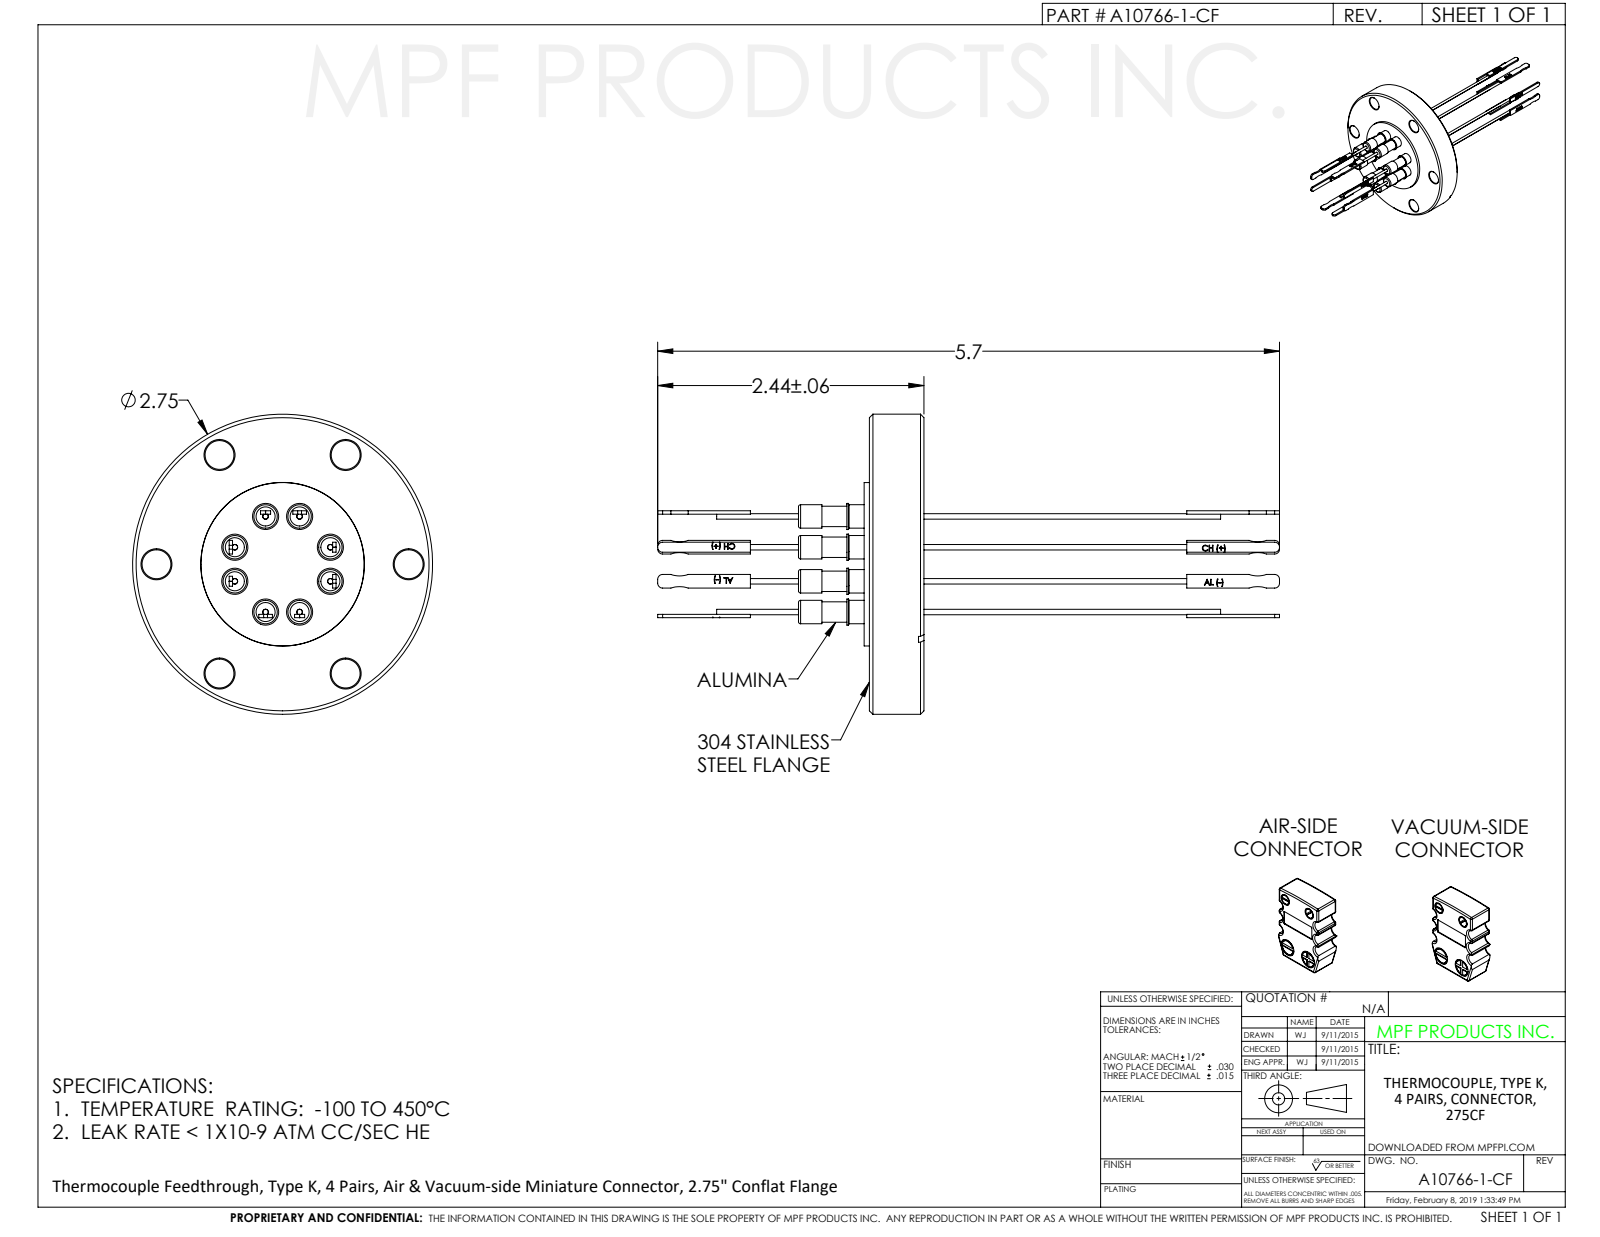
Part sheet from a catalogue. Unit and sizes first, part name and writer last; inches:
Units: inches
Overall size (bounding box): 5.308 × 2.75 × 2.75
Round holes (diameter × count): ⌀0.05 ×16, ⌀0.052 ×8, ⌀0.157 ×8, ⌀0.172 ×8, ⌀0.182 ×8, ⌀0.19 ×8, ⌀0.191 ×8, ⌀0.055 ×6, ⌀0.265 ×6, ⌀0.055 ×2, ⌀1.427 ×1, ⌀1.5 ×1
Round bosses / shafts (diameter × count): ⌀0.215 ×8, ⌀0.187 ×8, ⌀0.179 ×8, ⌀2.75 ×1, ⌀1.497 ×1
Partial cylindrical surfaces — rounded edges, fillets, slot ends (radius × count): R0.03 ×16, R0.046 ×8, R0.065 ×8, R0.079 ×8, R1.655 ×2
Main face-to-face distances: 0.5, 0.051, 0.551, 0.125, 0.074, 0.426, 0.03, 0.449, 0.375, 0.031
Hole centre spacings: 1.156, 0.312, 0.876, 0.93, 0.465, 0.465, 0.467, 0.657
Volume: 2.356 in³ · Surface area: 42.63 in²
Bodies: 50 solids, 653 faces (215 planar, 319 cylindrical, 119 other)
Part name (STEP PRODUCT): A10766-1-CF
STEP written by: SolidWorks 2014 (CONFIG_CONTROL_DESIGN)
